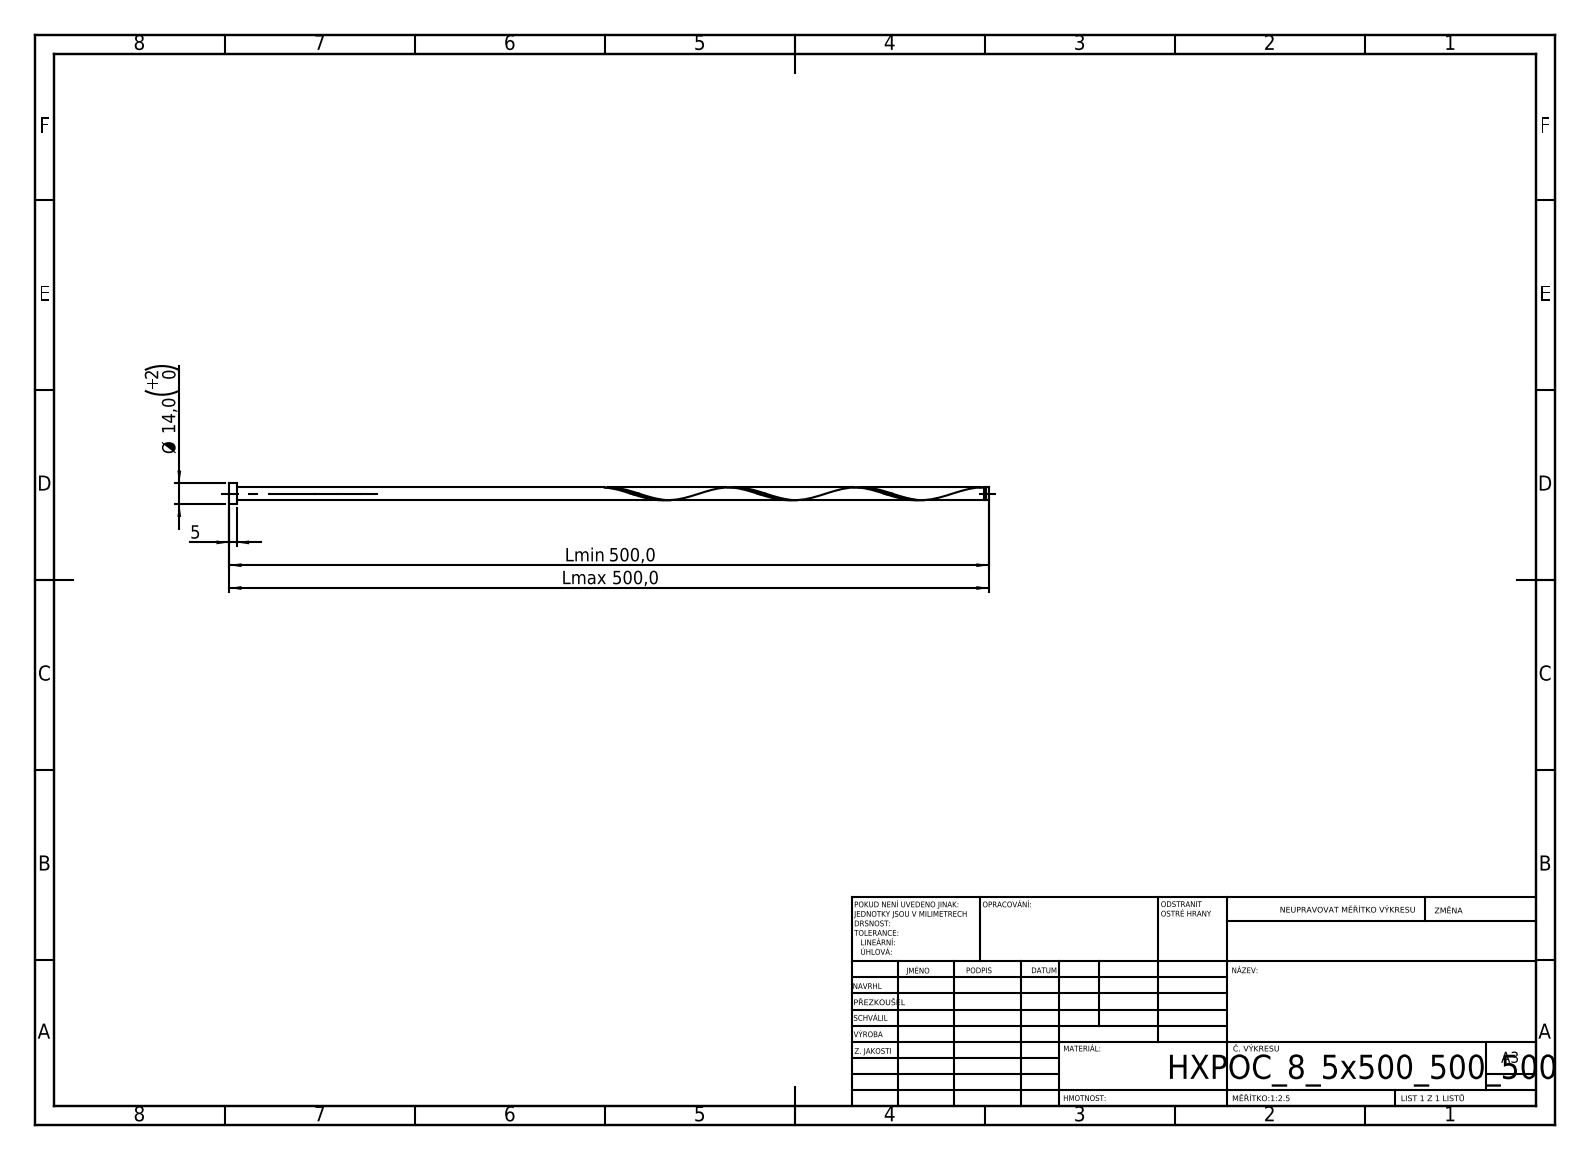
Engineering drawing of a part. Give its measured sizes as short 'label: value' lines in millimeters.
written by: SolidWorks 2019 (CONFIG_CONTROL_DESIGN)
unit: mm
bodies: 1 solid, 16 faces (6 planar, 9 cylindrical, 1 other)
size: 500 × 14 × 14
volume: 34 856 mm³; area: 18 442 mm²
bosses: 1× ⌀14, 1× ⌀8.5, 1× ⌀6.8
face distances: 5, 500, 495, 498.29, 493.29, 1.71, 496.59, 491.59, 1.7, 3.41
